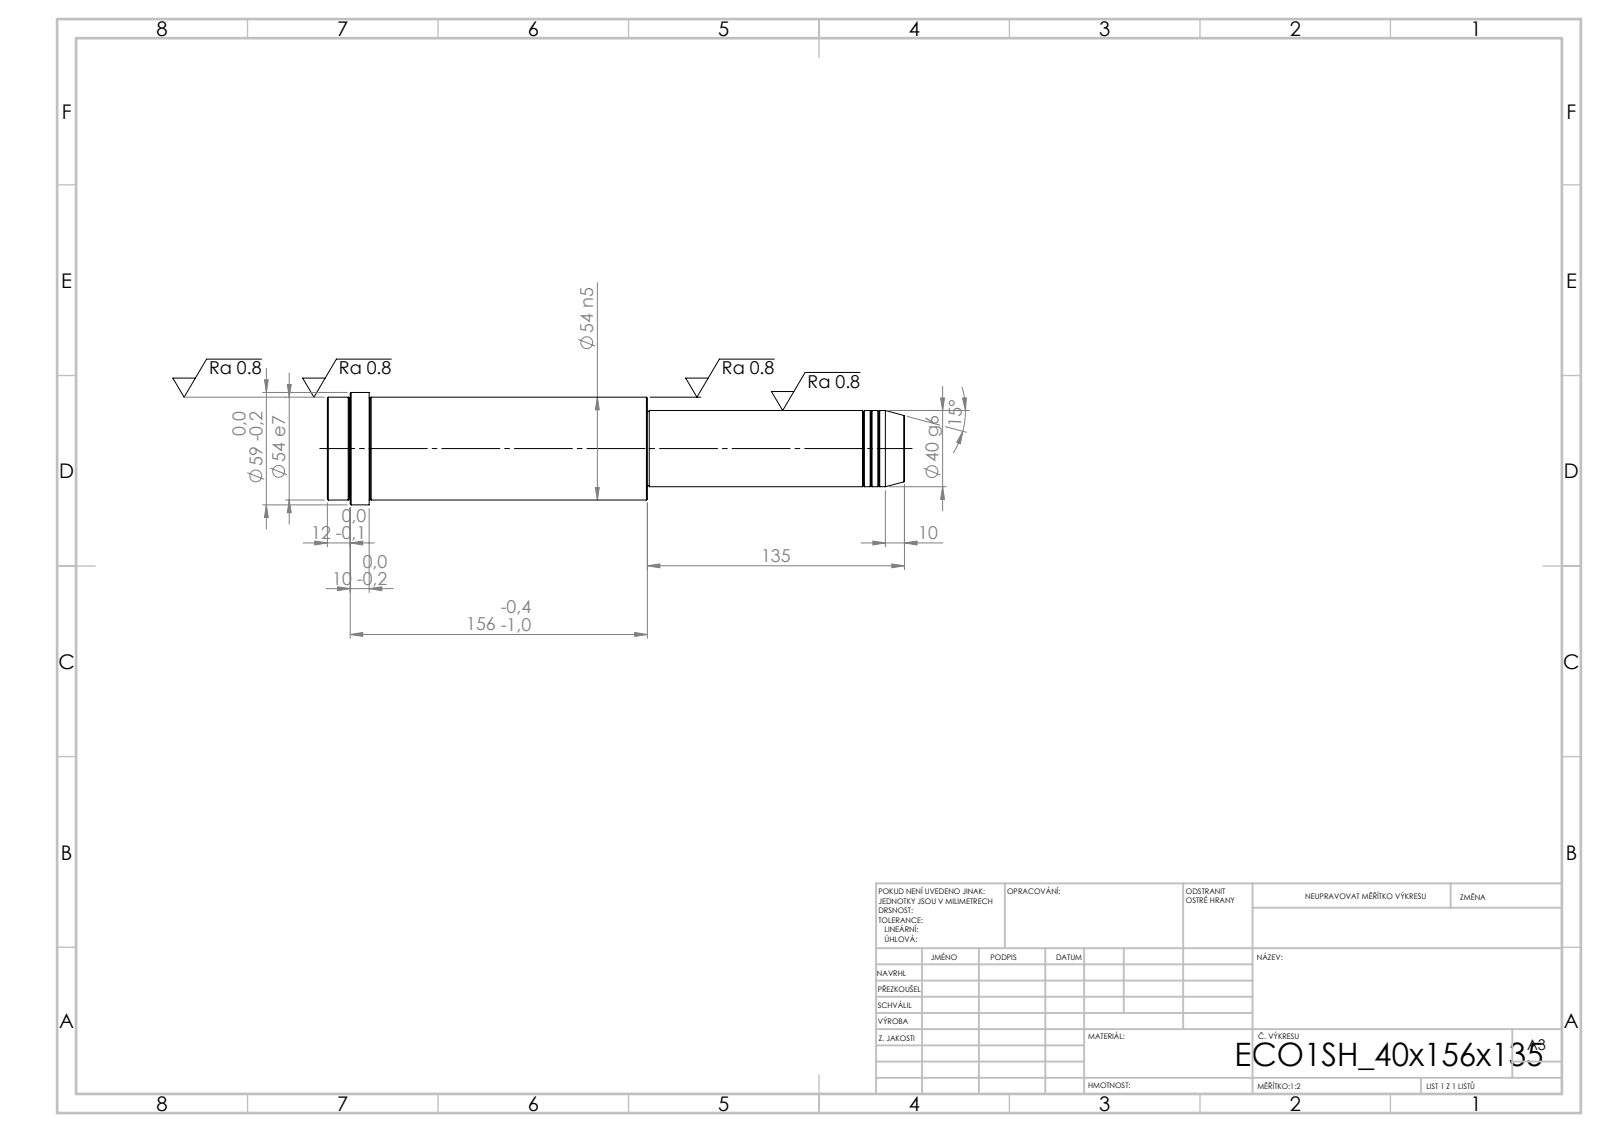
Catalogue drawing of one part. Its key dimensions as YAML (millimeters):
step_written_by: "SolidWorks 2019 (CONFIG_CONTROL_DESIGN)"
units: millimeters
bodies: {solids: 1, faces: 52, planar: 6, cylindrical: 16, other: 30}
overall_size: [303, 59, 59]
volume: 556823
surface_area: 51080
round_bosses_or_shafts:
  - {diameter: 59, count: 1}
  - {diameter: 54, count: 1}
  - {diameter: 40, count: 1}
  - {diameter: 39, count: 1}
face_to_face_distances: [168, 135, 303, 281, 146, 22, 291, 156, 10, 12]
